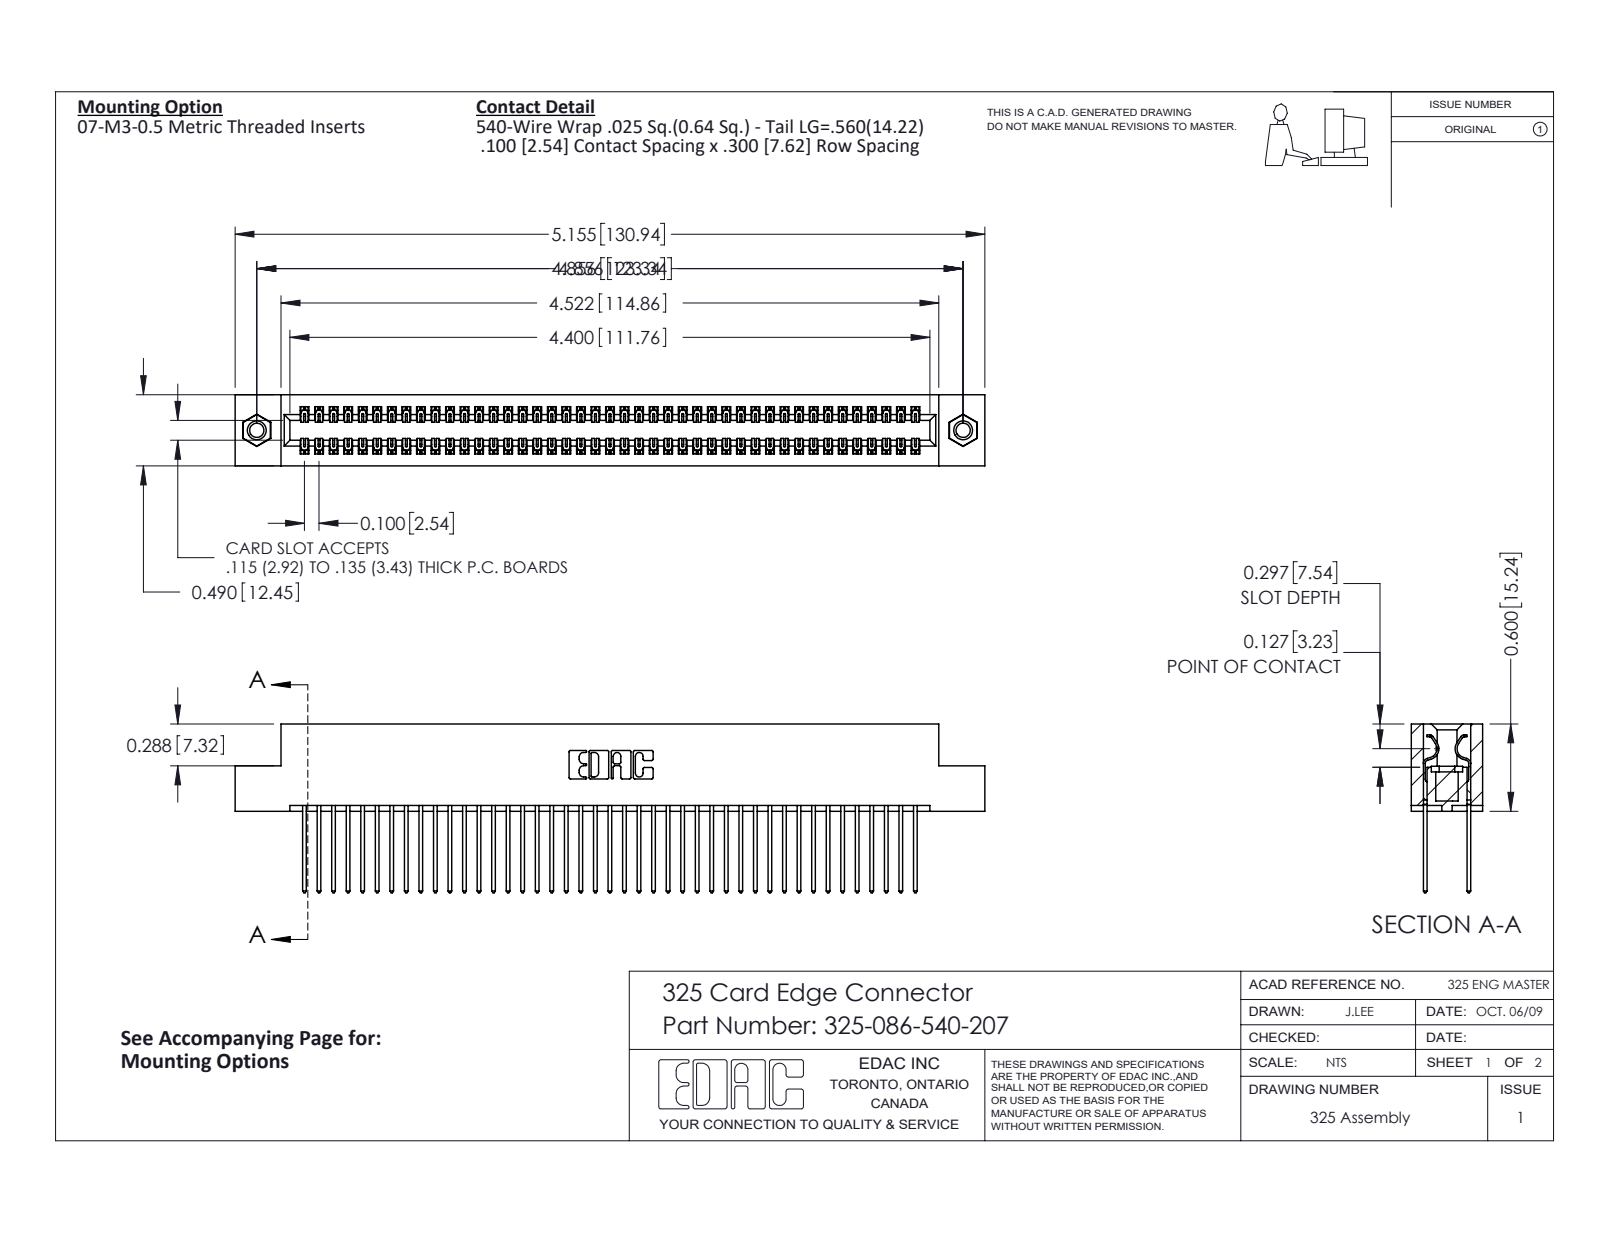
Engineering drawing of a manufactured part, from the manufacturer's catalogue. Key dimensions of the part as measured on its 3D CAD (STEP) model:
Part name (STEP PRODUCT): 325 Part_TI; 345-250-001_345-250-005-103; 325-292-001_325-293-140; 325-086-540-207
STEP written by: SolidWorks 2016 (CONFIG_CONTROL_DESIGN)
Units: inches
Bodies: 89 solids, 4646 faces (3198 planar, 1432 cylindrical, 16 other)
Overall size (bounding box): 5.155 × 1.16 × 0.49
Volume: 1.051 in³ · Surface area: 34.8 in²
Round holes (diameter × count): ⌀0.098 ×2, ⌀0.125 ×2, ⌀0.16 ×2
Round bosses / shafts (diameter × count): ⌀0.155 ×2
Partial cylindrical surfaces — rounded edges, fillets, slot ends (radius × count): R0.006 ×129, R0.01 ×86, R0.01 ×22, R0.007 ×6, R0.031 ×6, R0.026 ×3, R0.014 ×2, R0.022 ×2
Main face-to-face distances: 0.083, 0.407, 0.3, 0.107, 0.383, 0.025, 0.49, 0.325, 0.275, 0.56
Hole centre spacings: 4.856
